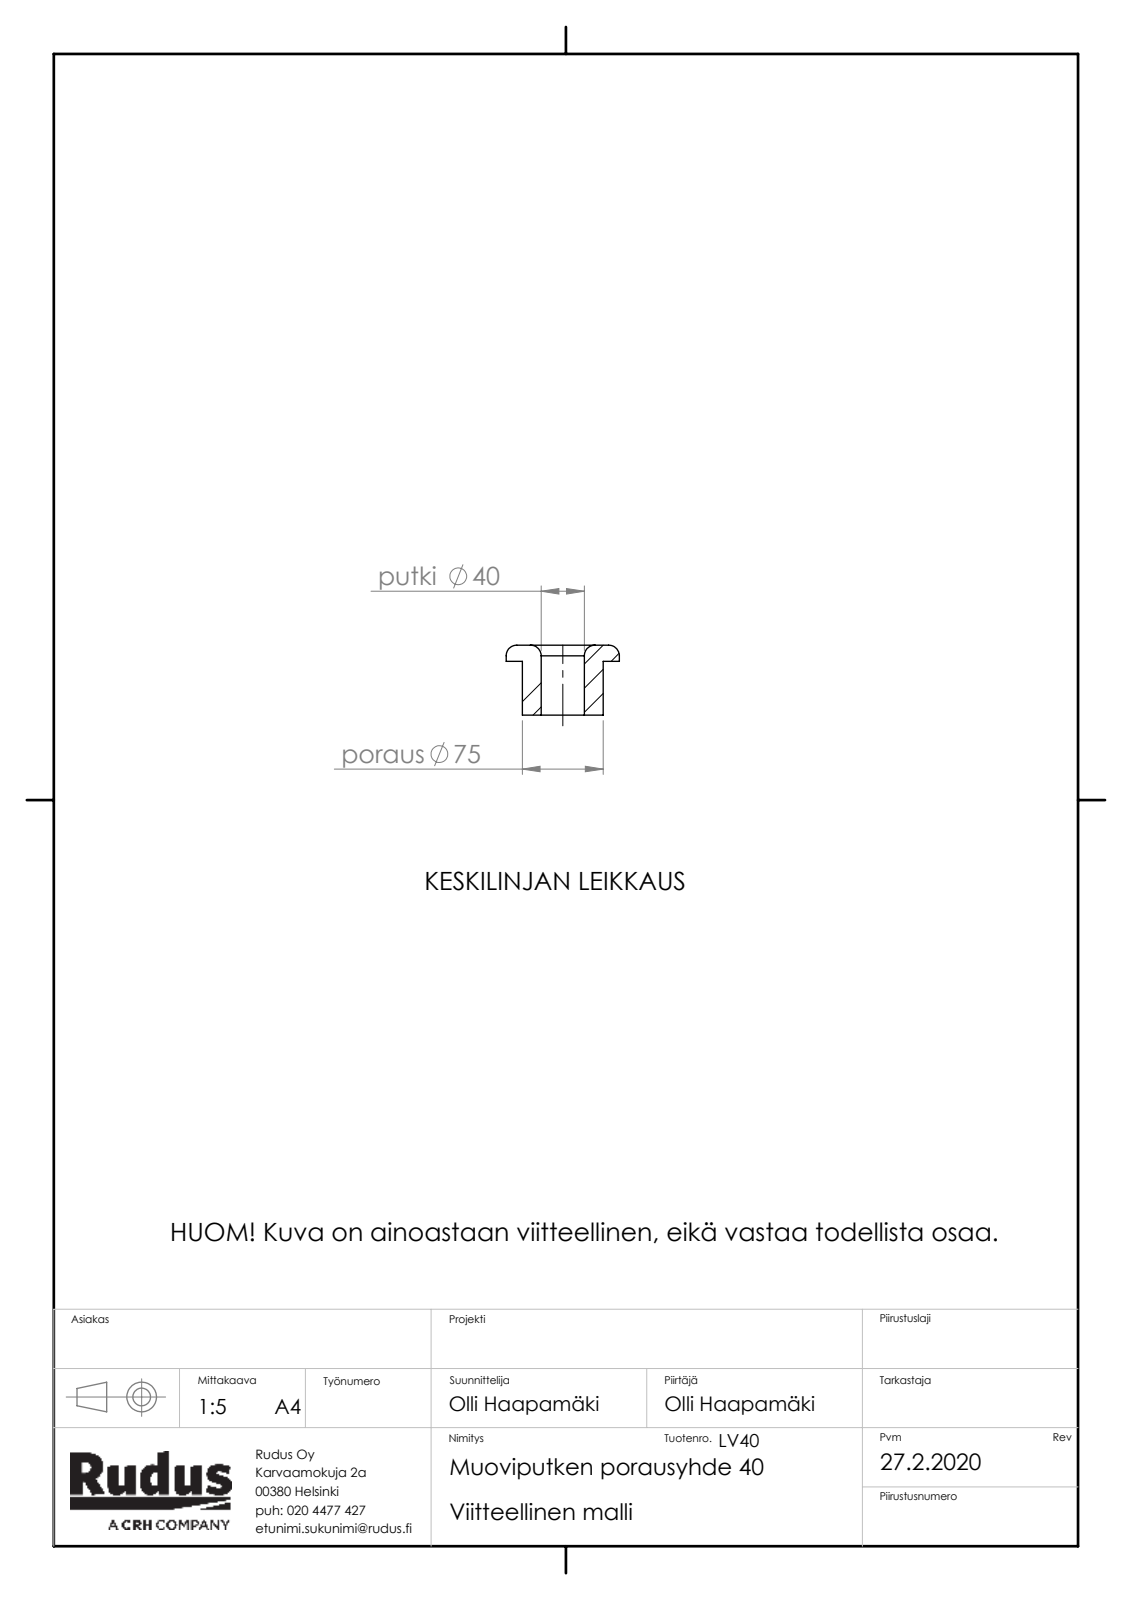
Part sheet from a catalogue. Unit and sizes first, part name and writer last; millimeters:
Units: millimetres
Overall size (bounding box): 105 × 105 × 65
Round holes (diameter × count): ⌀40 ×1
Round bosses / shafts (diameter × count): ⌀105 ×1, ⌀75 ×1
Main face-to-face distances: 50, 65, 15
Volume: 259 321 mm³ · Surface area: 37 747 mm²
Bodies: 1 solid, 13 faces (3 planar, 6 cylindrical, 4 other)
Part name (STEP PRODUCT): kaivo-muovi-lapivienti; Rudus LV40 Muoviputken porausyhde 40
STEP written by: SolidWorks 2019 (CONFIG_CONTROL_DESIGN)
